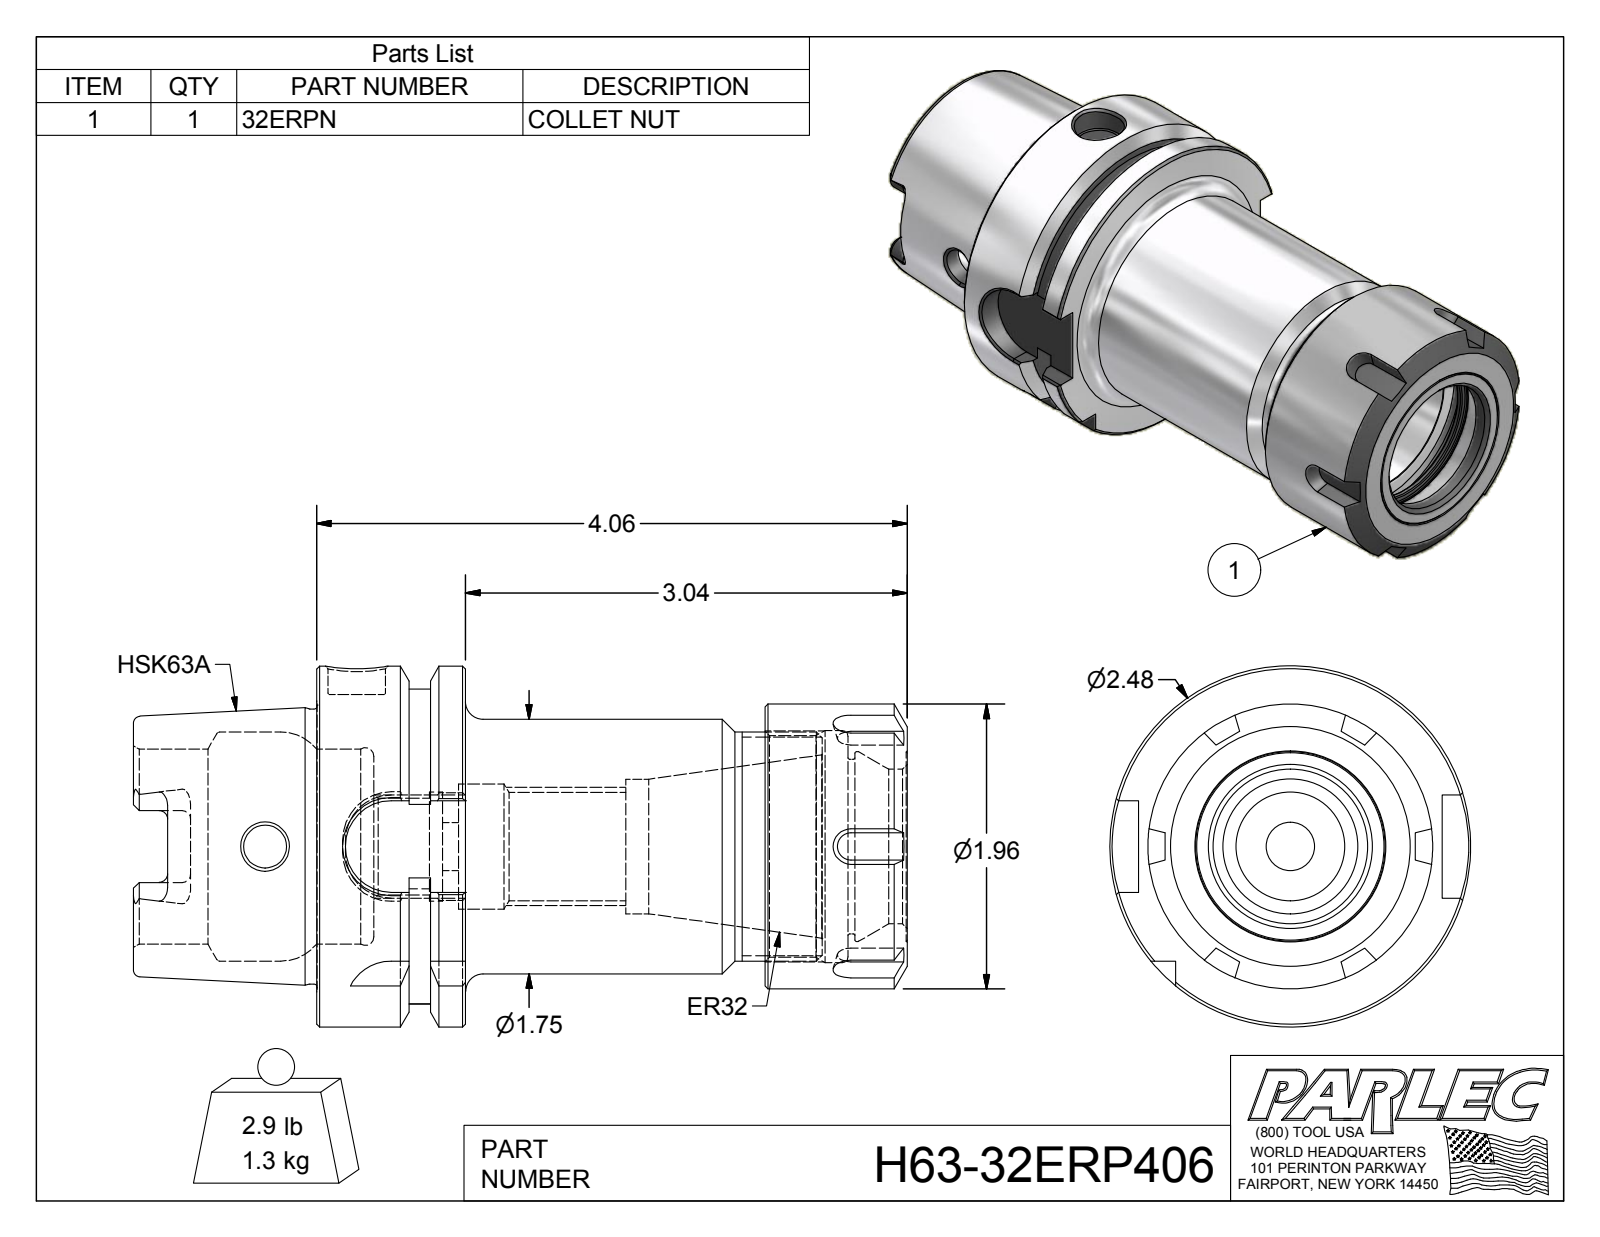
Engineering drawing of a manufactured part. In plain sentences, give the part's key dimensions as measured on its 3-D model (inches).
The part is named "H63-32ERP406; H63-32ER4-1; 32ERPN". Its 3-D file was written by "Autodesk Inventor 2012 (AUTOMOTIVE_DESIGN)". It is 2 solids with 188 faces: 76 planar, 43 cylindrical and 69 other. Overall it measures 5.32 by 2.48 by 2.48 inches. Its volume is 10.12 cubic inches and its surface area 68.86 square inches. Round holes: 1 of diameter 0.295, 1 of diameter 0.331, 1 of diameter 0.394, 1 of diameter 0.666, 1 of diameter 0.745, 1 of diameter 0.749, 1 of diameter 0.861, 1 of diameter 0.925, 1 of diameter 1.063, 1 of diameter 1.2, 1 of diameter 1.305, 1 of diameter 1.339. Round bosses or shafts: 1 of diameter 2.48, 1 of diameter 1.958, 1 of diameter 1.891, 1 of diameter 1.75. Partial cylindrical surfaces (rounded edges, fillets, slot ends): 6 of radius 0.059, 4 of radius 0.113, 4 of radius 0.315, 1 of radius 1.083. The main face-to-face distances are 1.024, 4.06, 3.036, 0.241, 0.389, 3.082, 2.058, 0.978, 0.394, 0.63.
